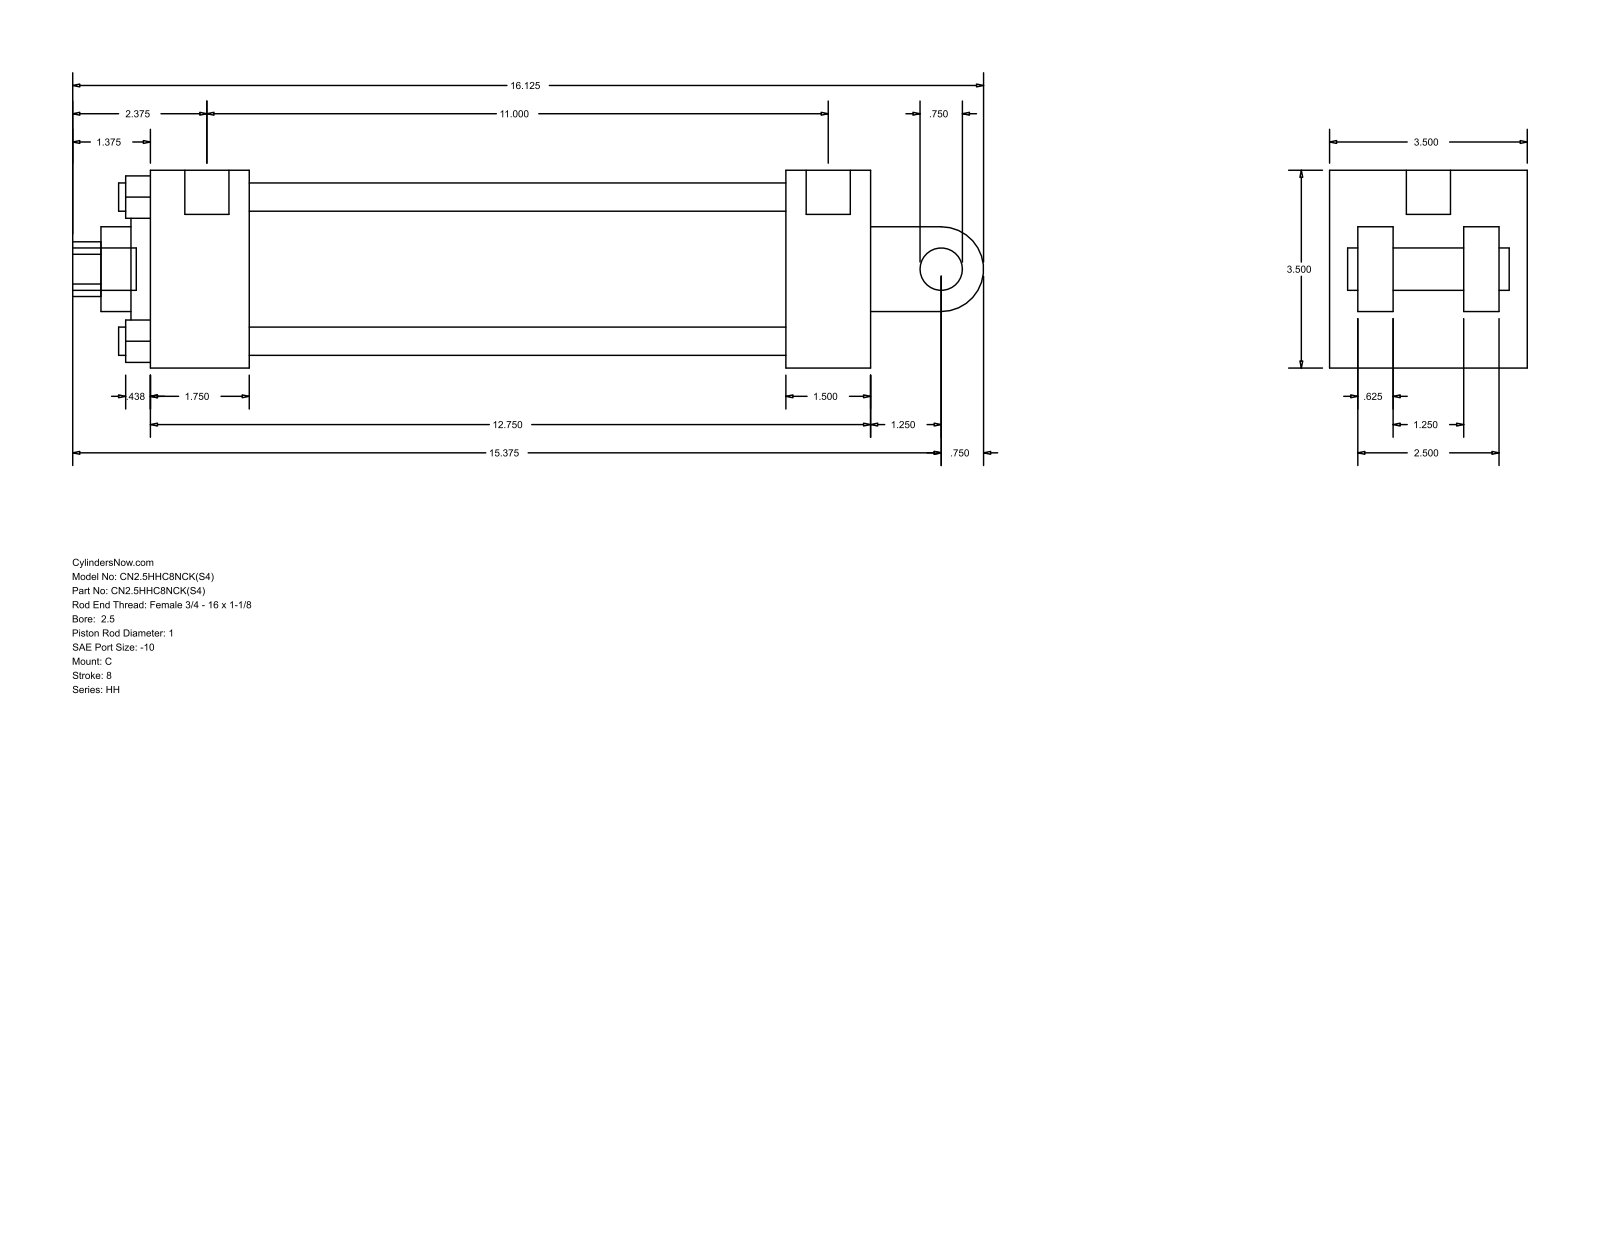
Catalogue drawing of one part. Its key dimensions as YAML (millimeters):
part_name: "HH_C__0250_1"
step_written_by: "GSSL Pune (CONFIG_CONTROL_DESIGN)"
units: millimeters
bodies: {solids: 0, faces: 101, planar: 71, cylindrical: 30, other: 0}
overall_size: [409.57, 88.9, 88.9]
round_holes:
  - {diameter: 12.7, count: 4}
  - {diameter: 5.56, count: 2}
  - {diameter: 19.84, count: 1}
  - {diameter: 25.4, count: 1}
  - {diameter: 38.1, count: 1}
  - {diameter: 60.33, count: 1}
  - {diameter: 73.03, count: 1}
round_bosses_or_shafts:
  - {diameter: 19.05, count: 2}
  - {diameter: 5.56, count: 2}
  - {diameter: 19.84, count: 1}
partial_cylinders:
  - {radius: 12.29, count: 1}
  - {radius: 19.05, count: 1}
face_to_face_distances: [88.9, 323.85, 63.5, 15.87, 285.76, 38.09, 44.46, 241.3, 279.39, 12.7]
hole_center_spacings: [45.79, 64.76, 91.58, 1.58]
